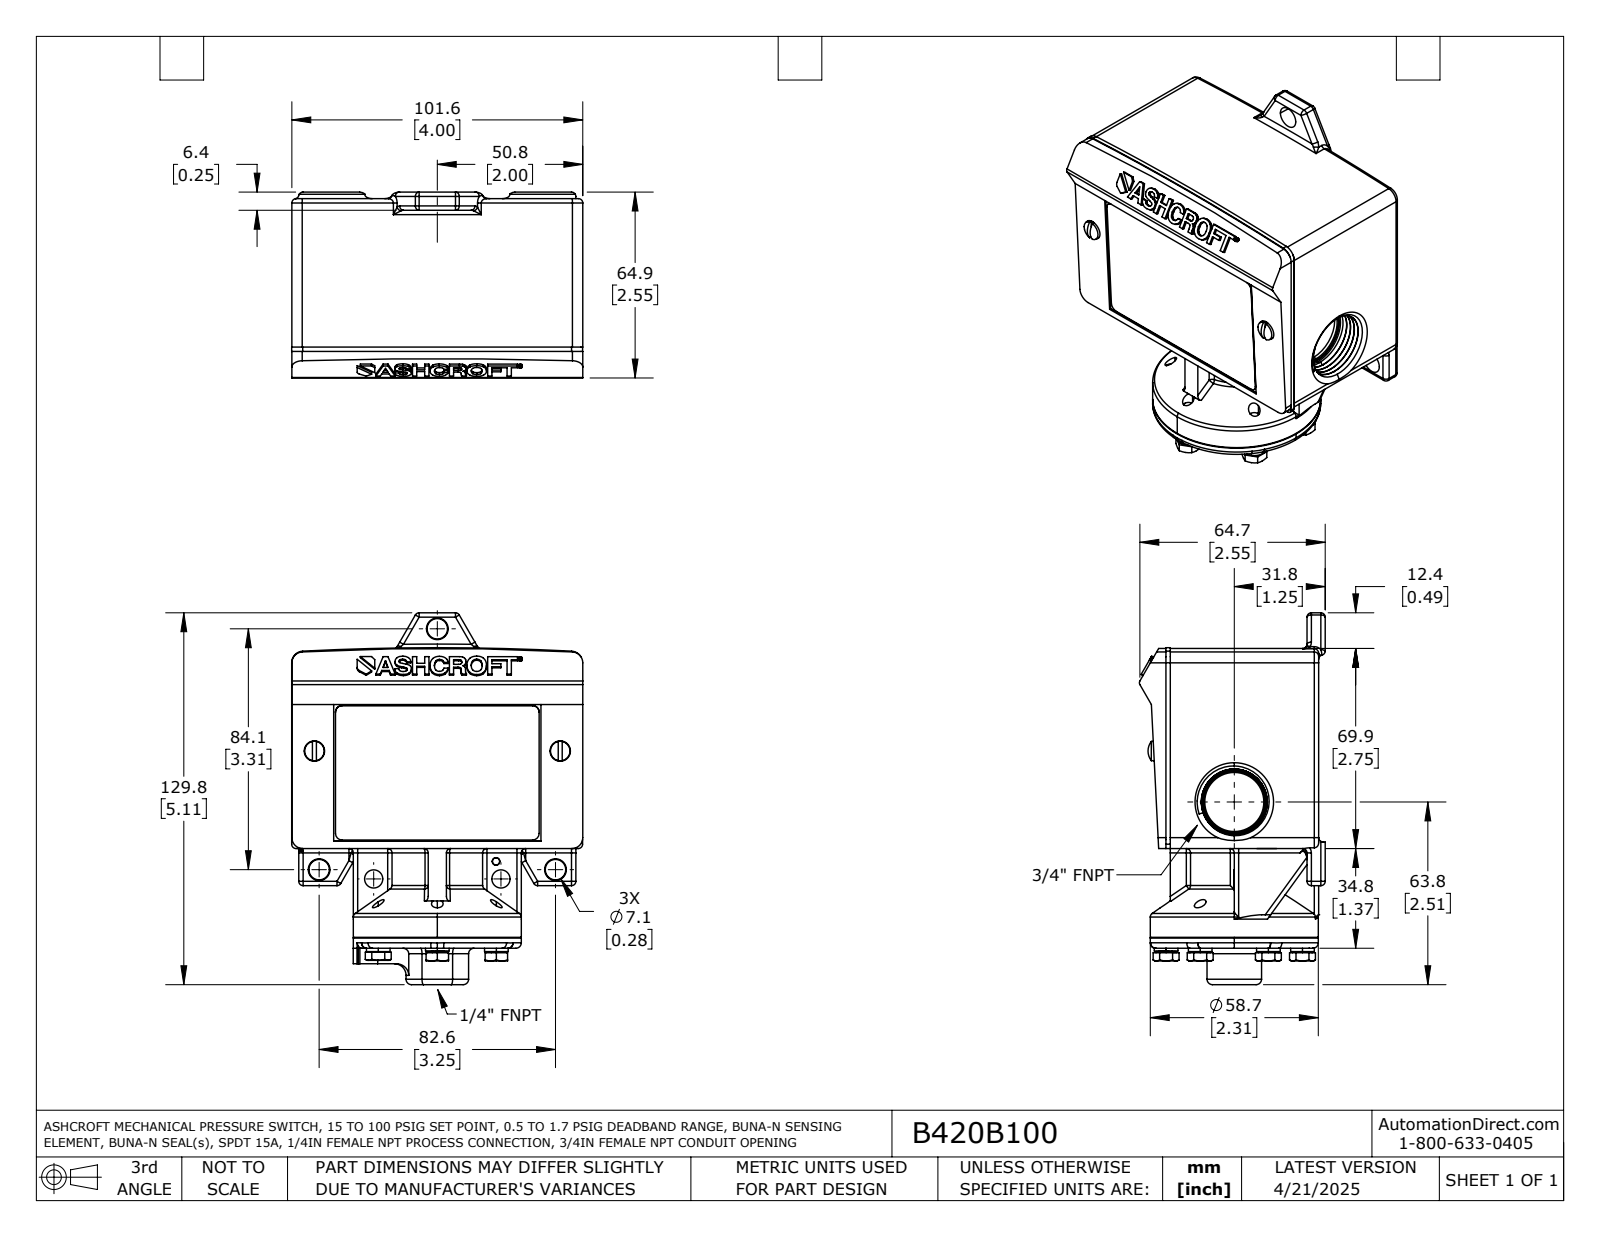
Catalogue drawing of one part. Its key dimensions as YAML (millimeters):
part_name: "B420B100"
step_written_by: "SolidWorks 2021 (AUTOMOTIVE_DESIGN)"
units: millimeters
bodies: {solids: 2, faces: 1259, planar: 345, cylindrical: 472, other: 442}
overall_size: [129.8, 101.7, 64.9]
volume: 468200
surface_area: 54520
round_holes:
  - {diameter: 4.1, count: 6}
  - {diameter: 4.9, count: 5}
  - {diameter: 5.3, count: 5}
  - {diameter: 4.7, count: 4}
  - {diameter: 7.1, count: 2}
  - {diameter: 11.6, count: 1}
  - {diameter: 20.6, count: 1}
round_bosses_or_shafts:
  - {diameter: 8.3, count: 6}
  - {diameter: 7.1, count: 6}
  - {diameter: 4.8, count: 5}
  - {diameter: 6.9, count: 2}
  - {diameter: 6.4, count: 2}
  - {diameter: 58.7, count: 1}
partial_cylinders:
  - {radius: 1.5, count: 92}
  - {radius: 0.8, count: 5}
  - {radius: 1.9, count: 4}
  - {radius: 2.3, count: 4}
  - {radius: 3.8, count: 4}
  - {radius: 0.3, count: 2}
  - {radius: 2.4, count: 2}
  - {radius: 4.1, count: 2}
face_to_face_distances: [101.6, 0.4, 34.8, 2.3, 99.3, 11.2, 90.4, 88.1, 8.9, 21.5]
hole_center_spacings: [23.8, 41.2, 47.6, 23.8, 85.9]
